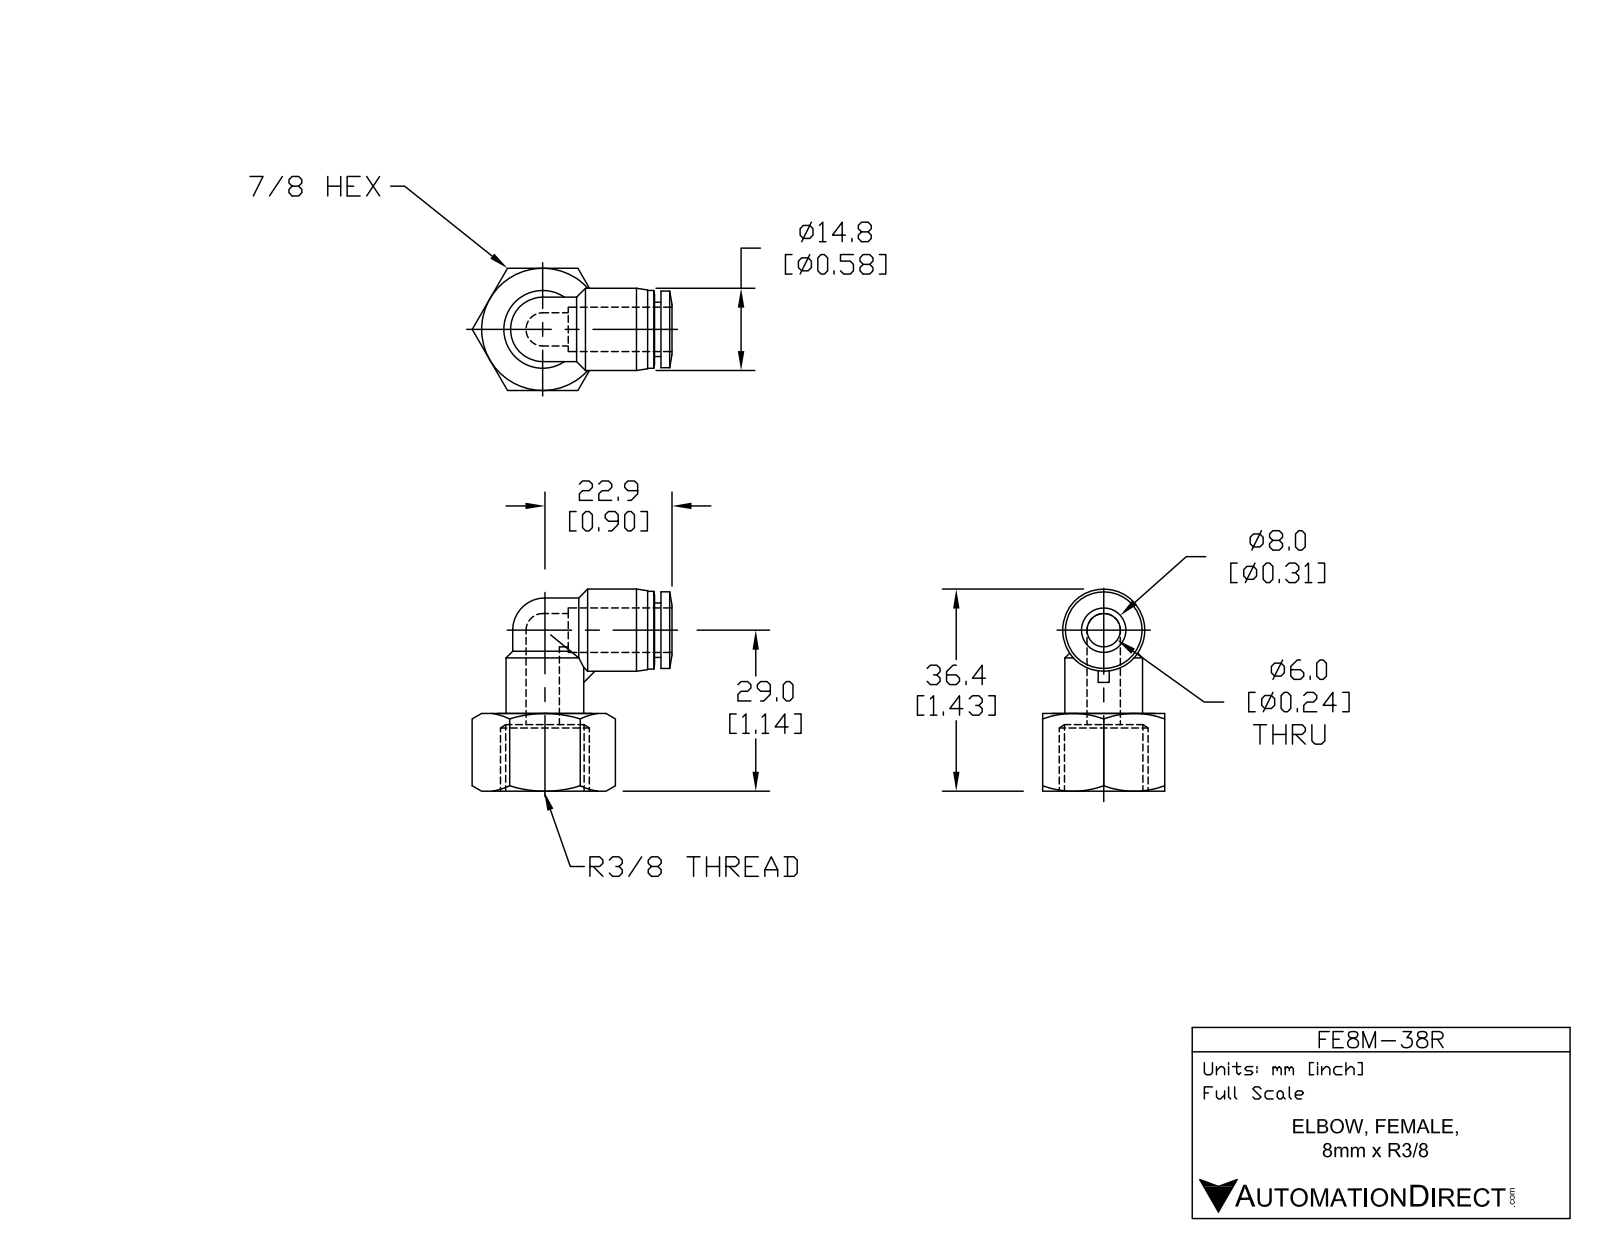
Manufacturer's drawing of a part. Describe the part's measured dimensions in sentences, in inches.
The part is named "FE8M-38R". Its 3-D file was written by "SolidWorks 2015 (AUTOMOTIVE_DESIGN)". It is 1 solid with 67 faces: 17 planar, 19 cylindrical and 31 other. Overall it measures 1.433 by 1.402 by 0.866 inches. Its volume is 0.43 cubic inches and its surface area 7.752 square inches. Round holes: 2 of diameter 0.236, 1 of diameter 0.327. Round bosses or shafts: 2 of diameter 0.551, 1 of diameter 0.583, 1 of diameter 0.543, 1 of diameter 0.457, 1 of diameter 0.386. Partial cylindrical surfaces (rounded edges, fillets, slot ends): 1 of radius 0.228. The main face-to-face distances are 0.866, 0.079, 0.472, 0.551, 0.045, 0.596, 0.642, 0.72, 0.124, 0.394.
